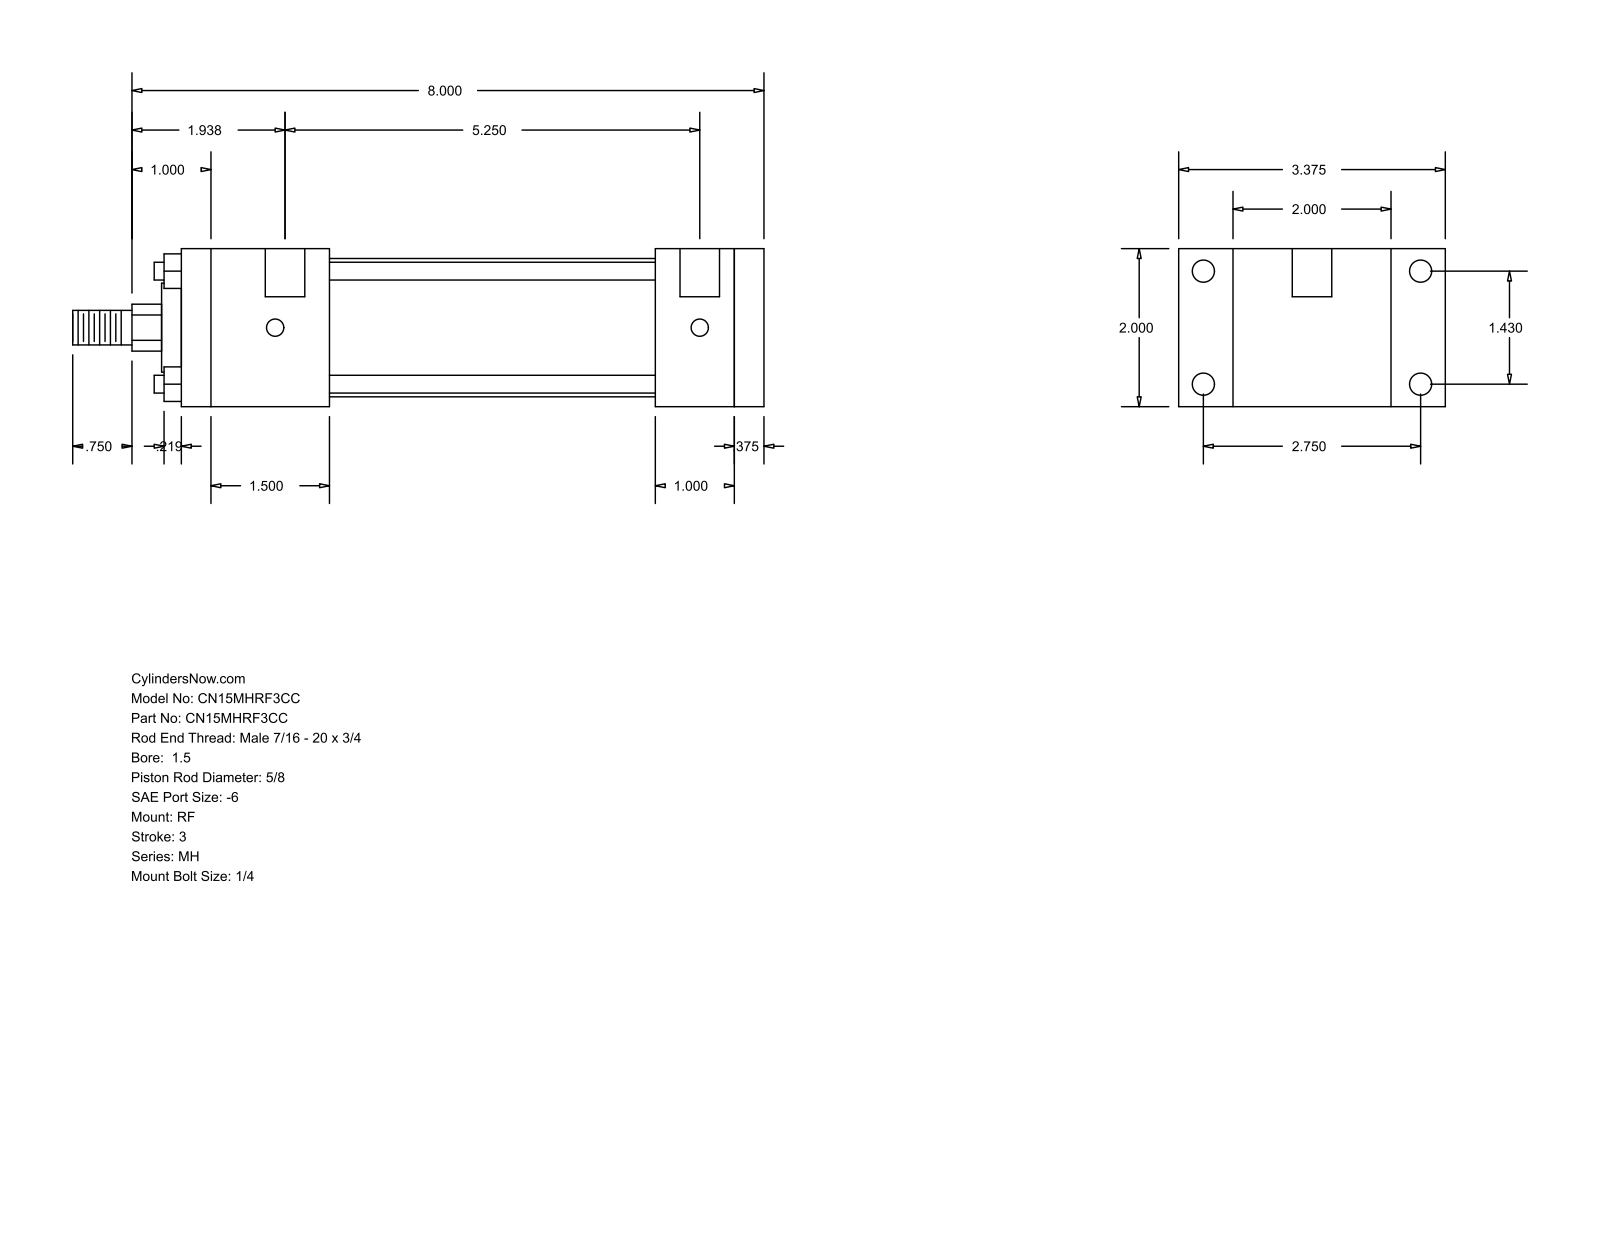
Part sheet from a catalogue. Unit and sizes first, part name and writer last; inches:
Units: inches
Overall size (bounding box): 8.75 × 3.375 × 2
Round holes (diameter × count): ⌀0.219 ×4, ⌀0.281 ×4, ⌀0.5 ×2
Round bosses / shafts (diameter × count): ⌀0.225 ×4, ⌀1.75 ×1, ⌀1.125 ×1, ⌀0.625 ×1, ⌀0.437 ×1
Partial cylindrical surfaces — rounded edges, fillets, slot ends (radius × count): R0.297 ×1
Main face-to-face distances: 2, 0.375, 7, 7.375, 1, 0.687, 2.687, 6, 1.375, 1.875
Hole centre spacings: 1.43, 2.75, 3.099, 5.375, 0.125, 5.25
Bodies: 0 solids, 92 faces (64 planar, 28 cylindrical, 0 other)
Part name (STEP PRODUCT): MH_RF__0150_0.625
STEP written by: GSSL Pune (CONFIG_CONTROL_DESIGN)
